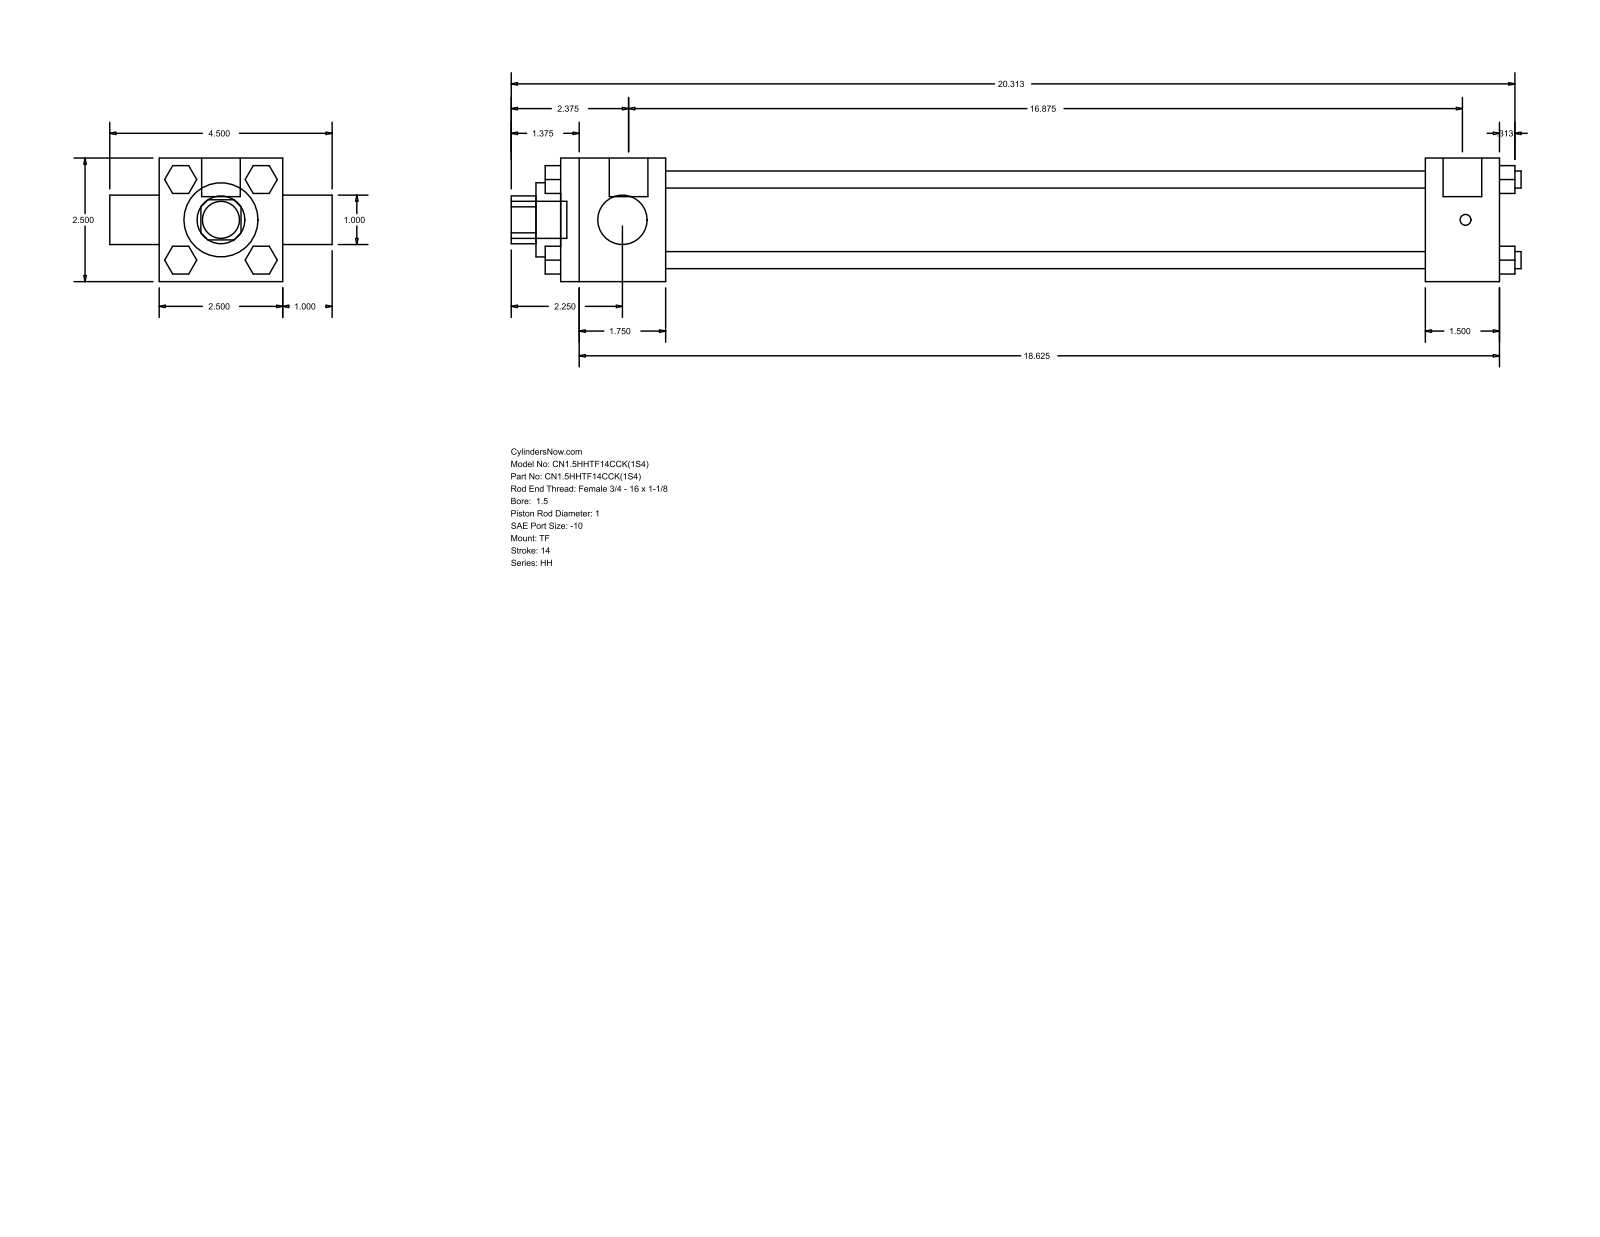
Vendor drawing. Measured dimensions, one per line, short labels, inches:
name: HH_TF__0150_1
written by: GSSL Pune (CONFIG_CONTROL_DESIGN)
unit: in
bodies: 0 solids, 120 faces (92 planar, 28 cylindrical, 0 other)
size: 20.437 × 4.5 × 2.5
holes: 2× ⌀1, 1× ⌀1.5, 1× ⌀1.75
bosses: 4× ⌀0.345, 3× ⌀0.219, 2× ⌀0.781, 1× ⌀0.75
rounds: 1× R0.484
face distances: 2.5, 16.875, 15.375, 1.5, 2.125, 17.5, 19, 19.313, 1, 0.815
